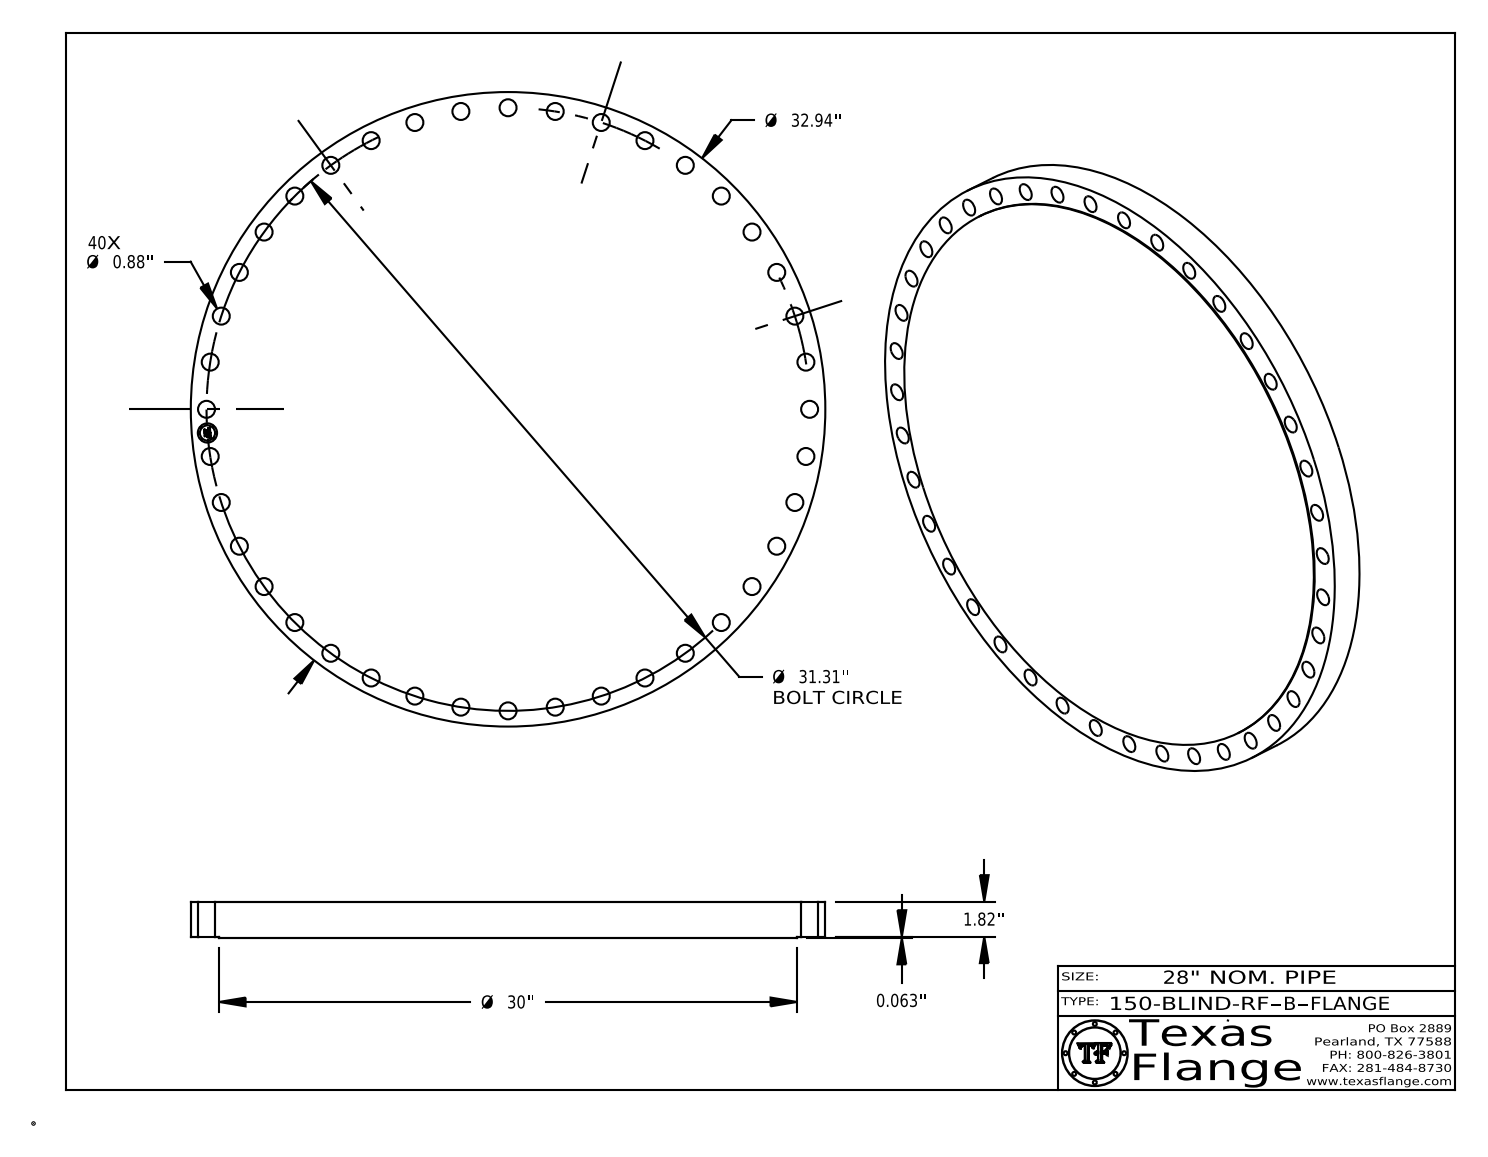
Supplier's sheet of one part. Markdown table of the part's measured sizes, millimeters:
| quantity | value |
| --- | --- |
| part name | 150-BLIND-RF, Series B |
| STEP written by | CATIA V5 STEP AP214 (AUTOMOTIVE_DESIGN) |
| units | millimeters |
| bodies | 1 solid, 472 faces (368 planar, 104 cylindrical, 0 other) |
| overall size | 836.7 × 836.7 × 47.8 |
| volume | 25 420 000 mm³ |
| surface area | 1 323 000 mm² |
| round holes (diameter × count) | 22.4 × 40, 25.4 × 1 |
| round bosses / shafts (diameter × count) | 1.5 × 8, 836.7 × 1, 762 × 1, 20 × 1 |
| main face-to-face distances | 47.8, 1.6, 46.2, 0.4, 47.4, 45.8, 7.6, 7.4, 0.5, 1.4 |
| hole center spacings | 124.4, 792.8, 304.3, 734.7, 62.4, 415.5, 516.5, 185.6 |
